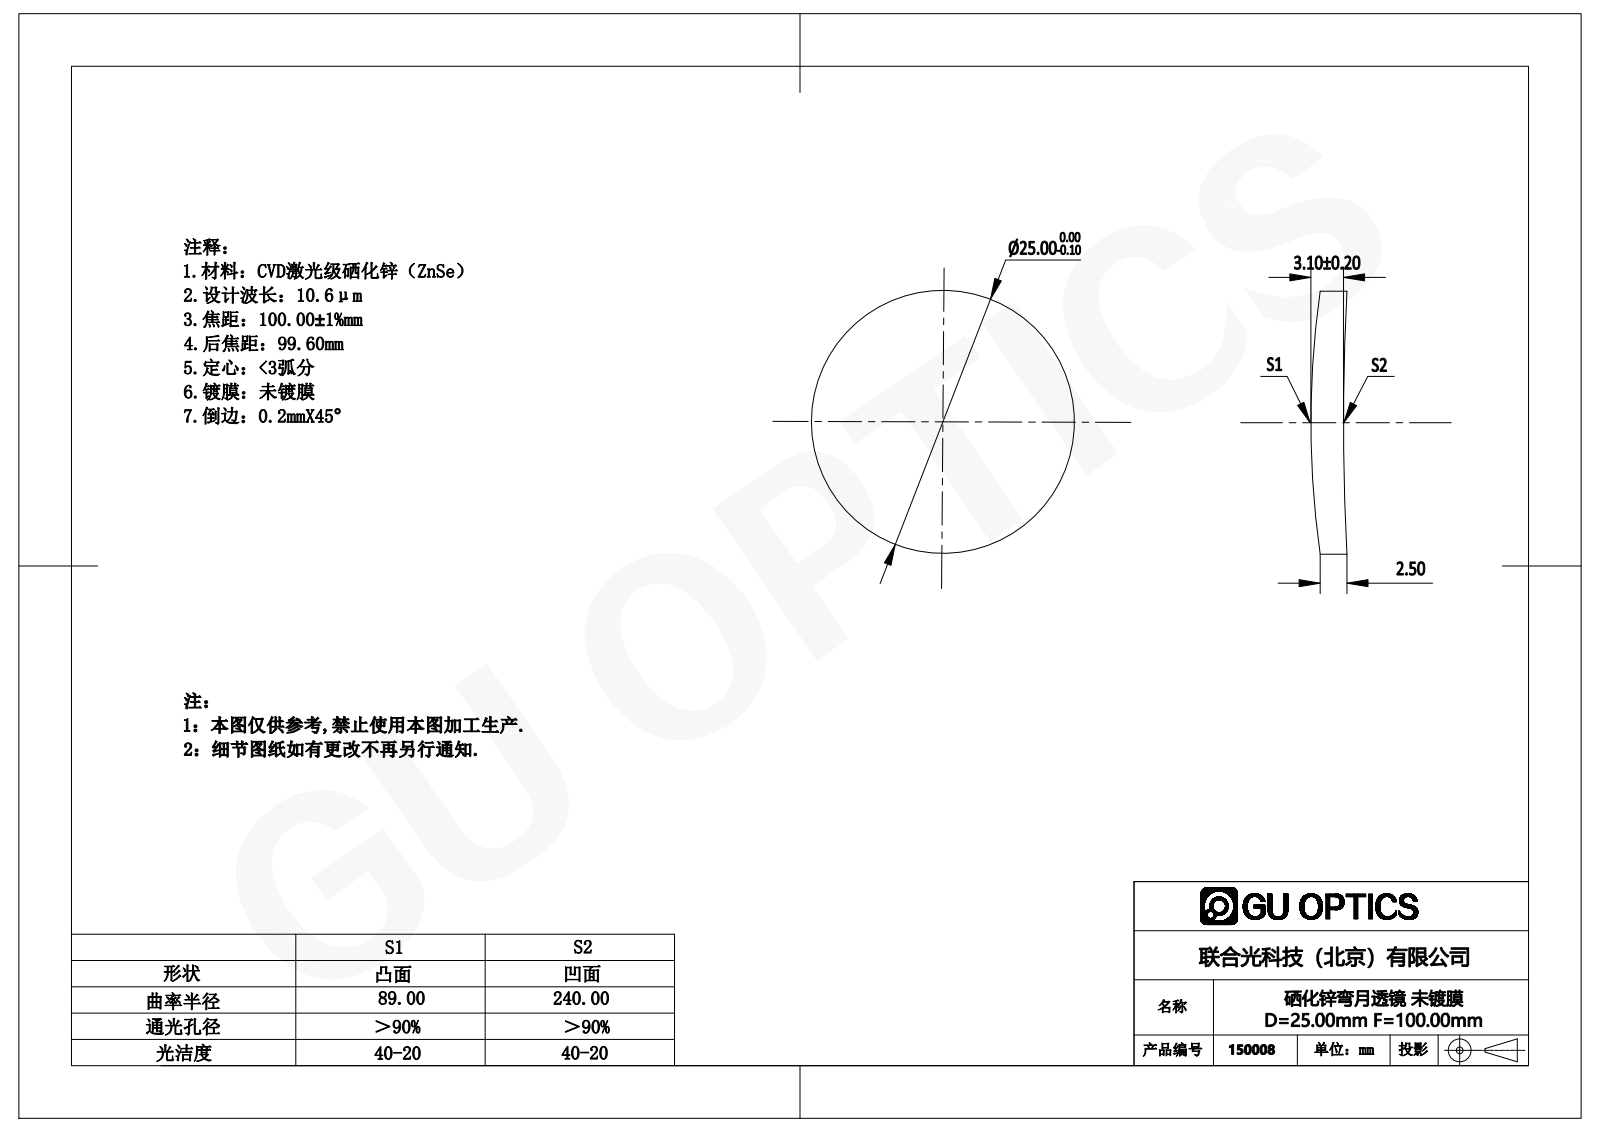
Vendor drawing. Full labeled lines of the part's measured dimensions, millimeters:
Part name (STEP PRODUCT): 150008
STEP written by: SolidWorks 2016 (AUTOMOTIVE_DESIGN)
Units: millimetres
Bodies: 1 solid, 6 faces (0 planar, 2 cylindrical, 4 other)
Overall size (bounding box): 25 × 25 × 3.43
Volume: 1 385 mm³ · Surface area: 1 184 mm²
Round bosses / shafts (diameter × count): ⌀25 ×1
